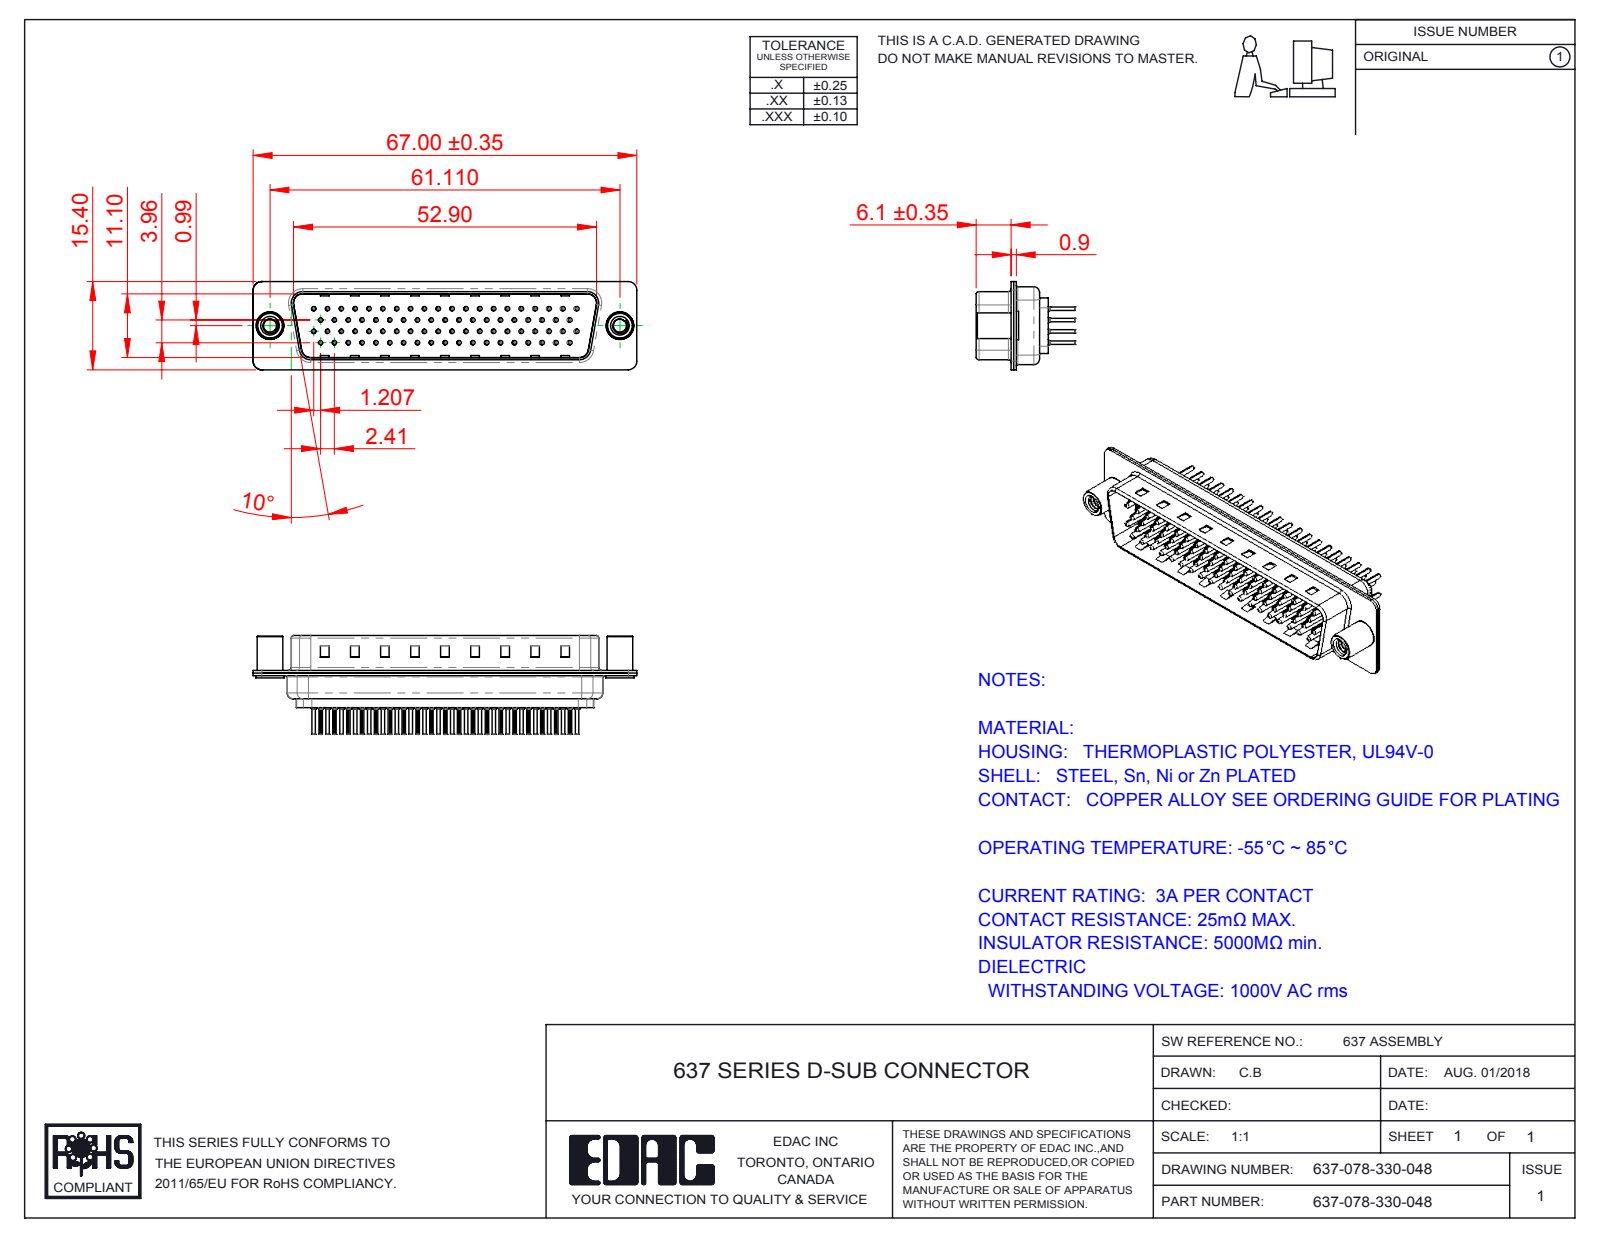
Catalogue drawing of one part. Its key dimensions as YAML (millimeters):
part_name: "637 Shell Rear_78 Contacts; 637 Shell Front_78 Contacts; 637 Contact Row 1_30; 637 Housing_78 Contacts (+5 more)"
step_written_by: "SolidWorks 2016 (CONFIG_CONTROL_DESIGN)"
units: millimeters
bodies: {solids: 83, faces: 8246, planar: 2077, cylindrical: 3055, other: 3114}
overall_size: [67, 17.25, 15.4]
volume: 4398
surface_area: 16058
round_holes:
  - {diameter: 1.6, count: 150}
  - {diameter: 0.2, count: 78}
  - {diameter: 0.35, count: 78}
  - {diameter: 1.1, count: 78}
  - {diameter: 0.75, count: 72}
  - {diameter: 2, count: 72}
  - {diameter: 4, count: 3}
  - {diameter: 2.26, count: 2}
  - {diameter: 4.8, count: 2}
round_bosses_or_shafts:
  - {diameter: 2, count: 78}
  - {diameter: 1.5, count: 78}
  - {diameter: 0.75, count: 78}
  - {diameter: 0.6, count: 78}
  - {diameter: 5, count: 2}
  - {diameter: 4.9, count: 2}
  - {diameter: 4.5, count: 2}
  - {diameter: 4.8, count: 1}
partial_cylinders:
  - {radius: 0.1, count: 156}
  - {radius: 1.5, count: 16}
  - {radius: 2, count: 12}
  - {radius: 0.5, count: 8}
  - {radius: 0.25, count: 4}
  - {radius: 0.55, count: 4}
  - {radius: 0.7, count: 4}
  - {radius: 0.95, count: 4}
face_to_face_distances: [0.45, 0.4, 1.5, 1.95, 11.9, 11.5, 0.7, 11.1, 0.9, 0.8]
hole_center_spacings: [2.41, 7.24, 6.06, 9.65, 6.96, 8.46, 14.54, 16.89]
